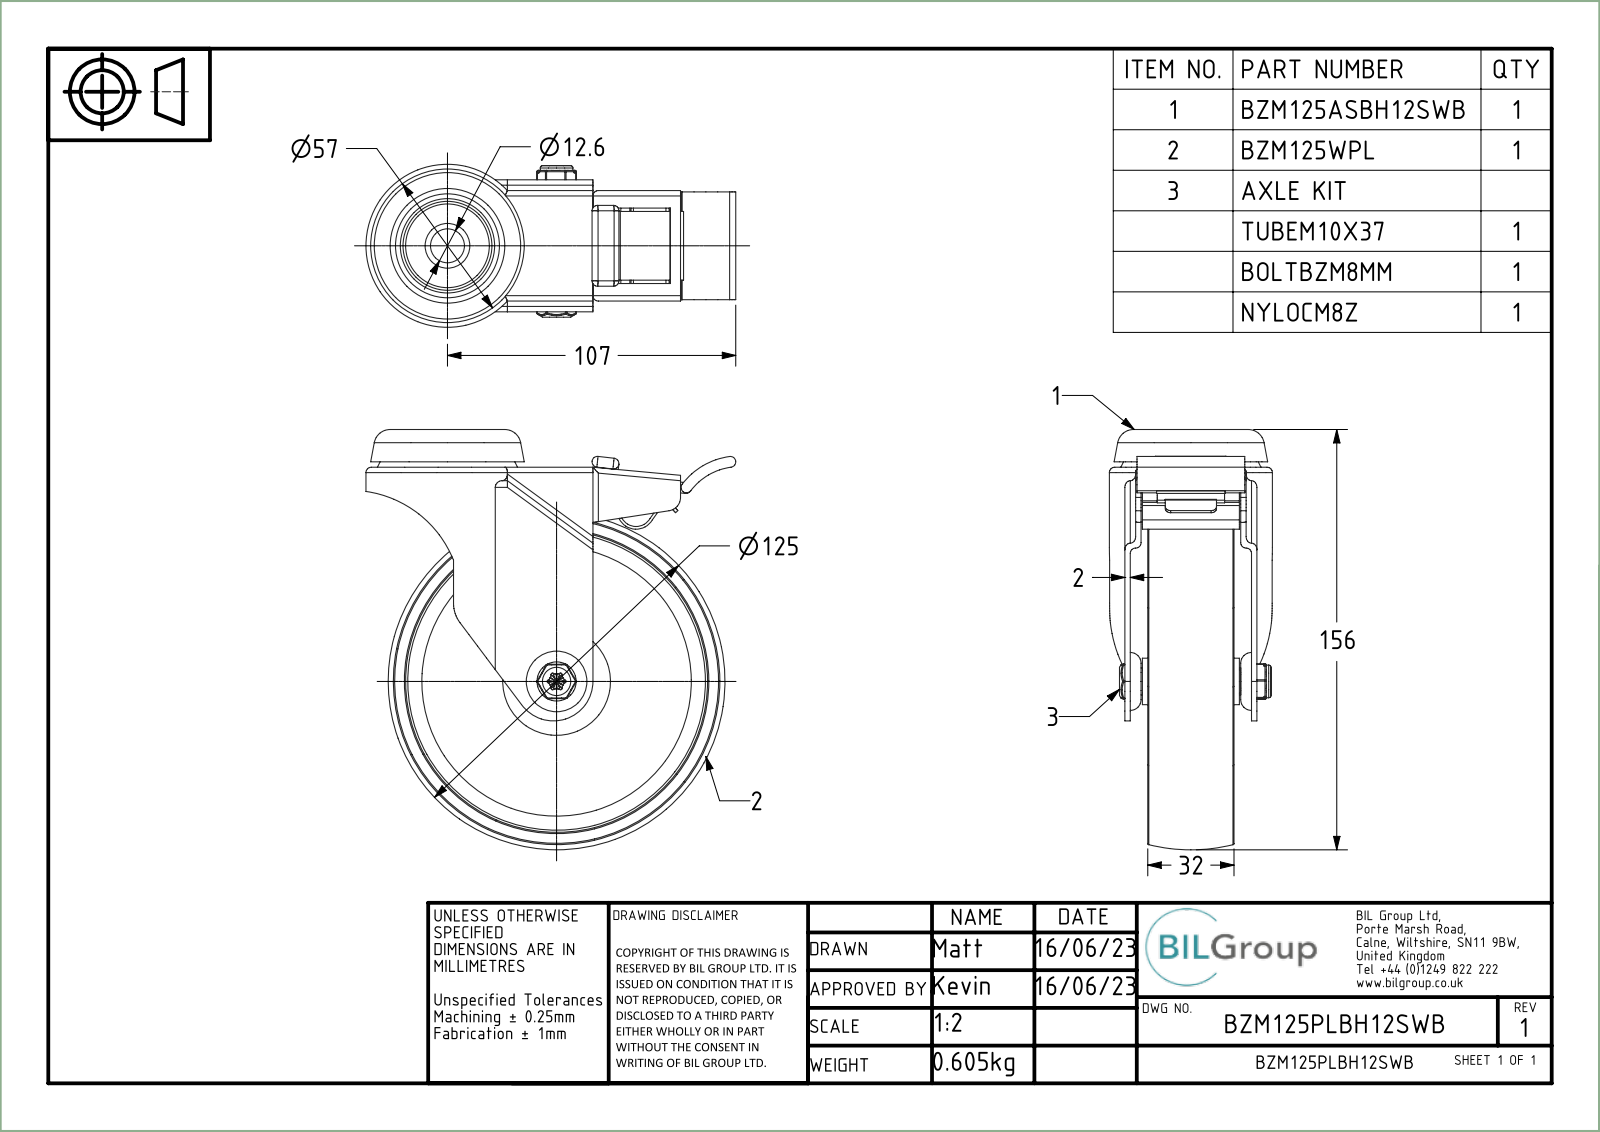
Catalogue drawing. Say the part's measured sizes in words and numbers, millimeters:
The part is named "BZM125ASBH12SWB; ZINC PLATED PRESSED STEEL HEAD; ZINC PLATED PRESSED STEEL FORKS; ZINC PLATED PRESSED STEEL BRAKE (+8 more)". Its 3-D file was written by "Spatial InterOp 3D (CONFIG_CONTROL_DESIGN)". It is 10 solids with 633 faces: 206 planar, 279 cylindrical and 148 other. Overall it measures 156 by 137.25 by 60.5 millimeters. Its volume is 174 394 cubic millimeters and its surface area 106 218 square millimeters. Round holes: 1 of diameter 8, 1 of diameter 8.2, 1 of diameter 8.5, 1 of diameter 8.6, 1 of diameter 10.2, 1 of diameter 10.3, 1 of diameter 12.6, 1 of diameter 46. Round bosses or shafts: 1 of diameter 48, 1 of diameter 30, 1 of diameter 17.25, 1 of diameter 12.1, 1 of diameter 10, 1 of diameter 6. Partial cylindrical surfaces (rounded edges, fillets, slot ends): 40 of radius 2, 30 of radius 0.5, 7 of radius 1, 4 of radius 6, 2 of radius 1.5, 2 of radius 3, 2 of radius 5, 1 of radius 0.88. The main face-to-face distances are 2, 4, 3.5, 43, 6, 22.75, 26.25, 41, 45, 47.
